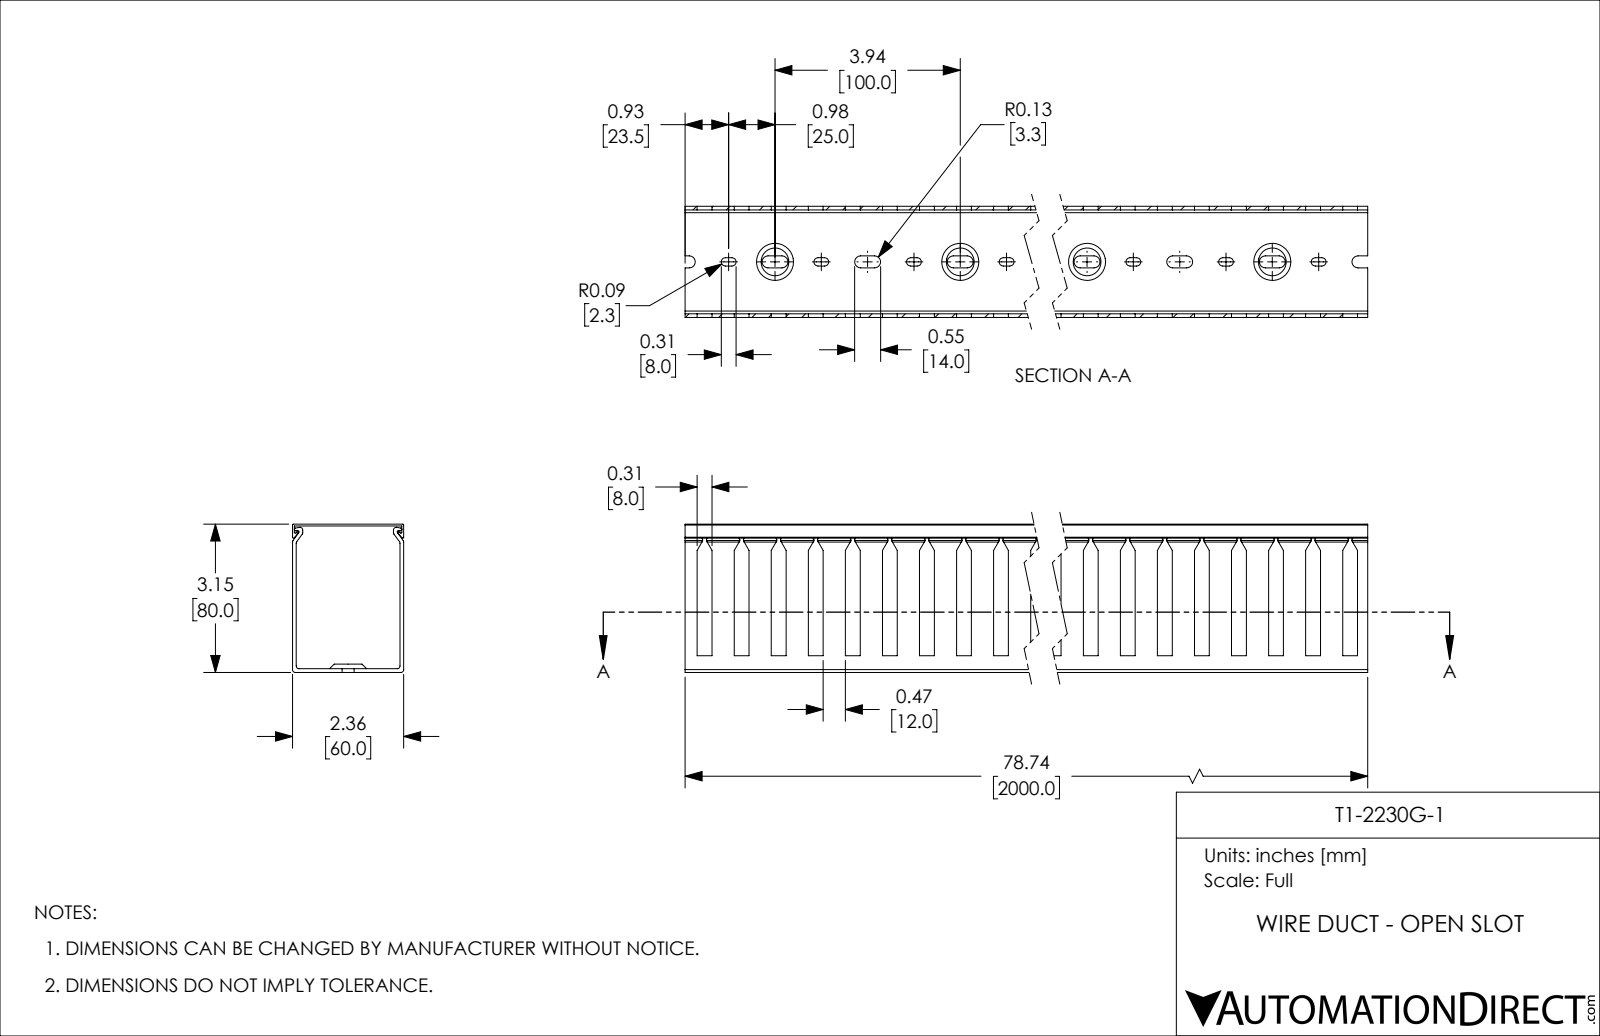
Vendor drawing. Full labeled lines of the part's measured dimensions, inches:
Part name (STEP PRODUCT): T1-2230G-1
STEP written by: SolidWorks 2021 (CONFIG_CONTROL_DESIGN)
Units: inches
Bodies: 2 solids, 1005 faces (534 planar, 431 cylindrical, 40 other)
Overall size (bounding box): 78.74 × 3.15 × 2.362
Volume: 61.51 in³ · Surface area: 1 809 in²
Partial cylindrical surfaces — rounded edges, fillets, slot ends (radius × count): R0.089 ×80, R0.128 ×80, R0.059 ×12, R0.02 ×8, R0.03 ×6
Main face-to-face distances: 0.079, 2.283, 2.362, 0.039, 2.205, 3.15, 3.11, 3.031, 3.071, 2.323
